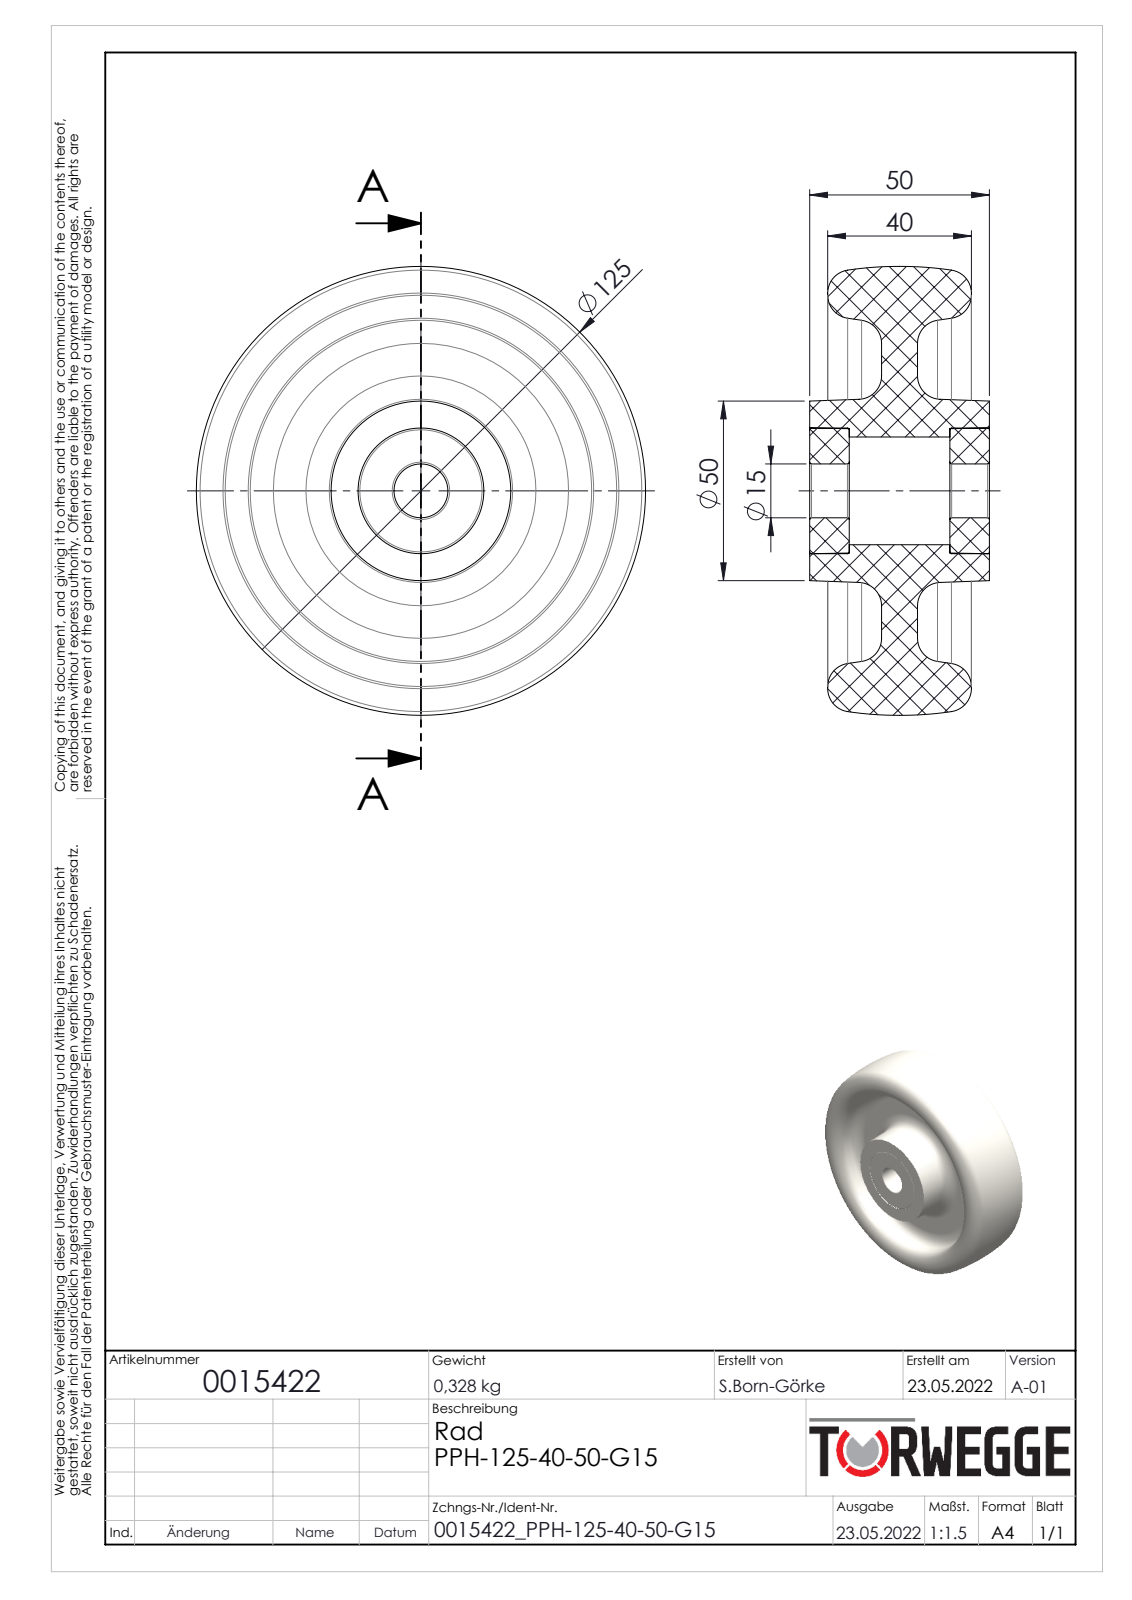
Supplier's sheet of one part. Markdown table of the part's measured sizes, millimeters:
| quantity | value |
| --- | --- |
| part name | 0015422 |
| STEP written by | SolidWorks 2020 (AUTOMOTIVE_DESIGN) |
| units | millimeters |
| bodies | 3 solids, 72 faces (10 planar, 10 cylindrical, 52 other) |
| overall size | 125 × 125 × 50 |
| volume | 320 676 mm³ |
| surface area | 58 032 mm² |
| round holes (diameter × count) | 15 × 1, 30 × 1 |
| round bosses / shafts (diameter × count) | 35 × 1 |
| main face-to-face distances | 20, 30, 10, 11, 39, 9, 19, 50, 28 |
